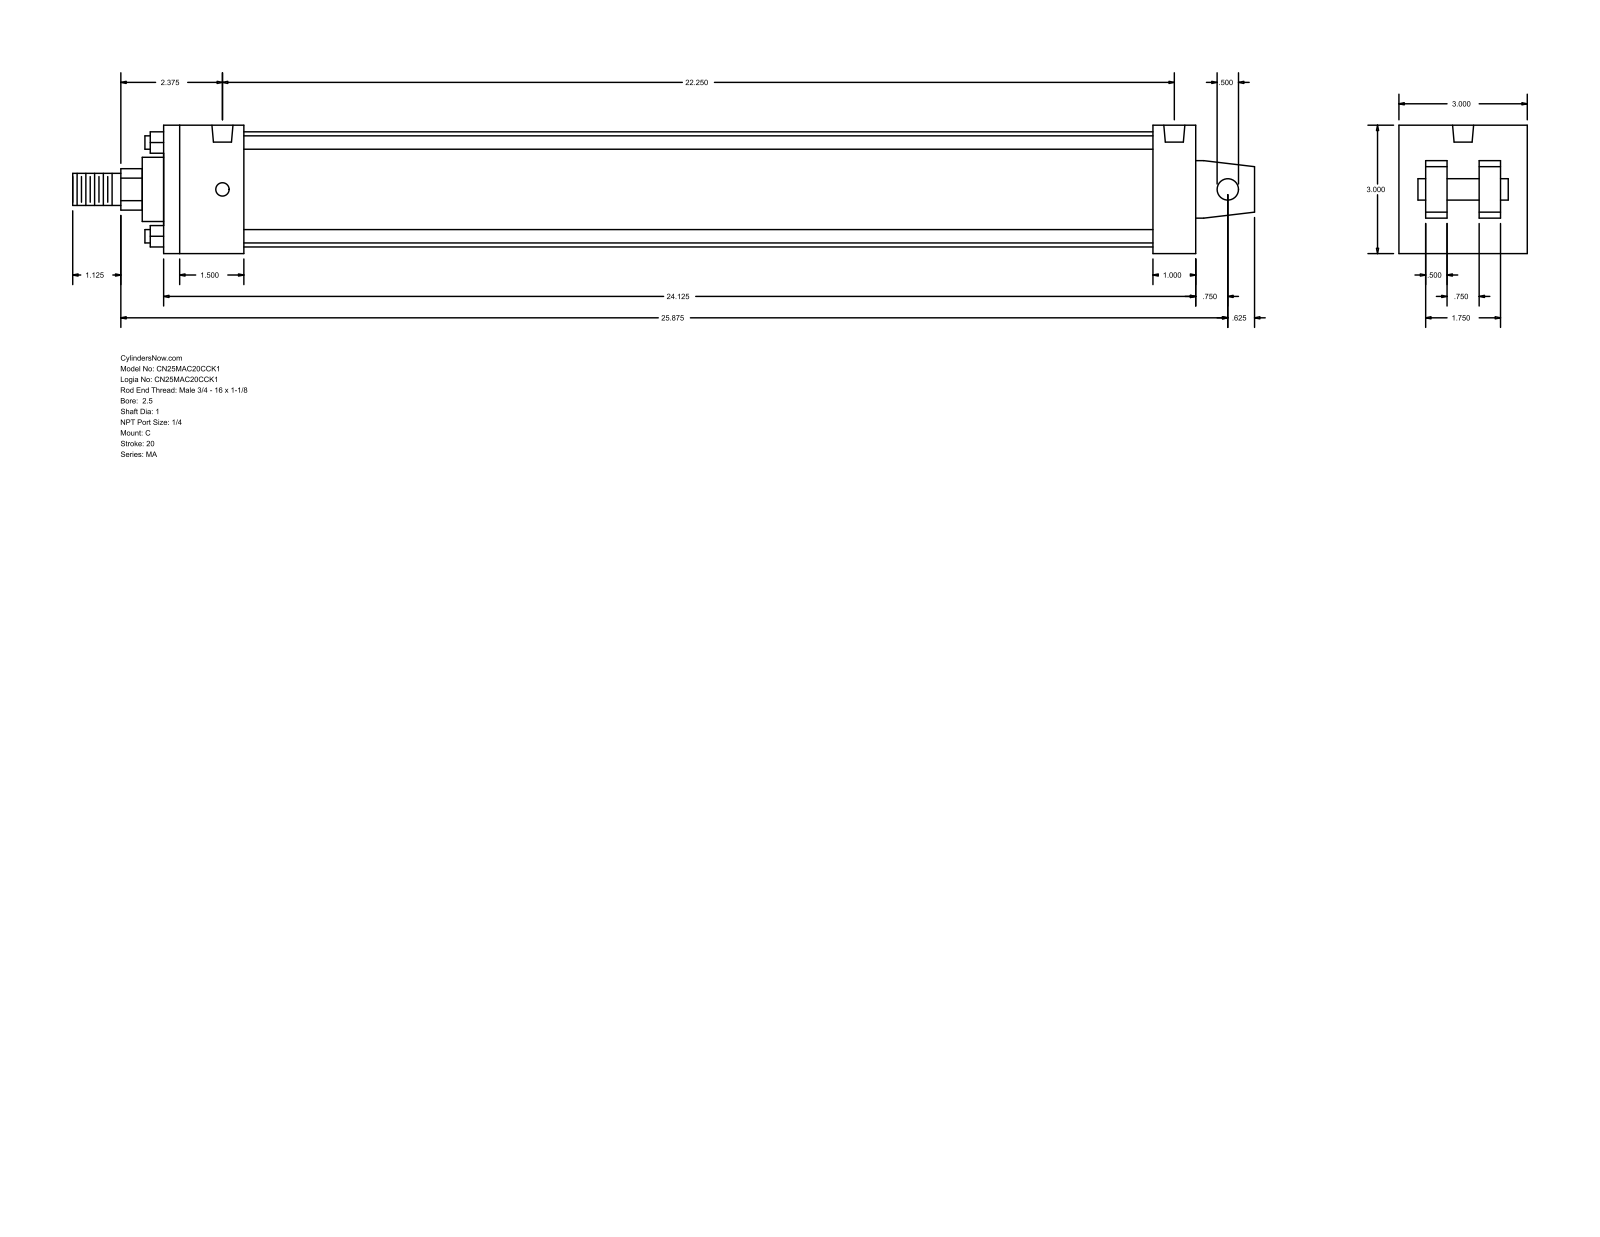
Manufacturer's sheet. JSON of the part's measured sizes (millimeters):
{"part_name": "MA_C__0250_1", "step_written_by": "GSSL Pune (CONFIG_CONTROL_DESIGN)", "units": "millimeters", "bodies": {"solids": 0, "faces": 103, "planar": 76, "cylindrical": 27, "other": 0}, "overall_size": [701.67, 76.2, 76.2], "round_holes": [[7.94, 4], [12.49, 2]], "round_bosses_or_shafts": [[7.94, 4], [68.33, 1], [38.1, 1], [25.4, 1], [19.05, 1], [12.7, 1]], "partial_cylinders_radius": [[12.29, 1]], "face_to_face_distances": [76.2, 612.77, 47.63, 12.7, 60.33, 15.87, 25.4, 28.57, 587.37, 539.74], "hole_center_spacings": [565.15]}
